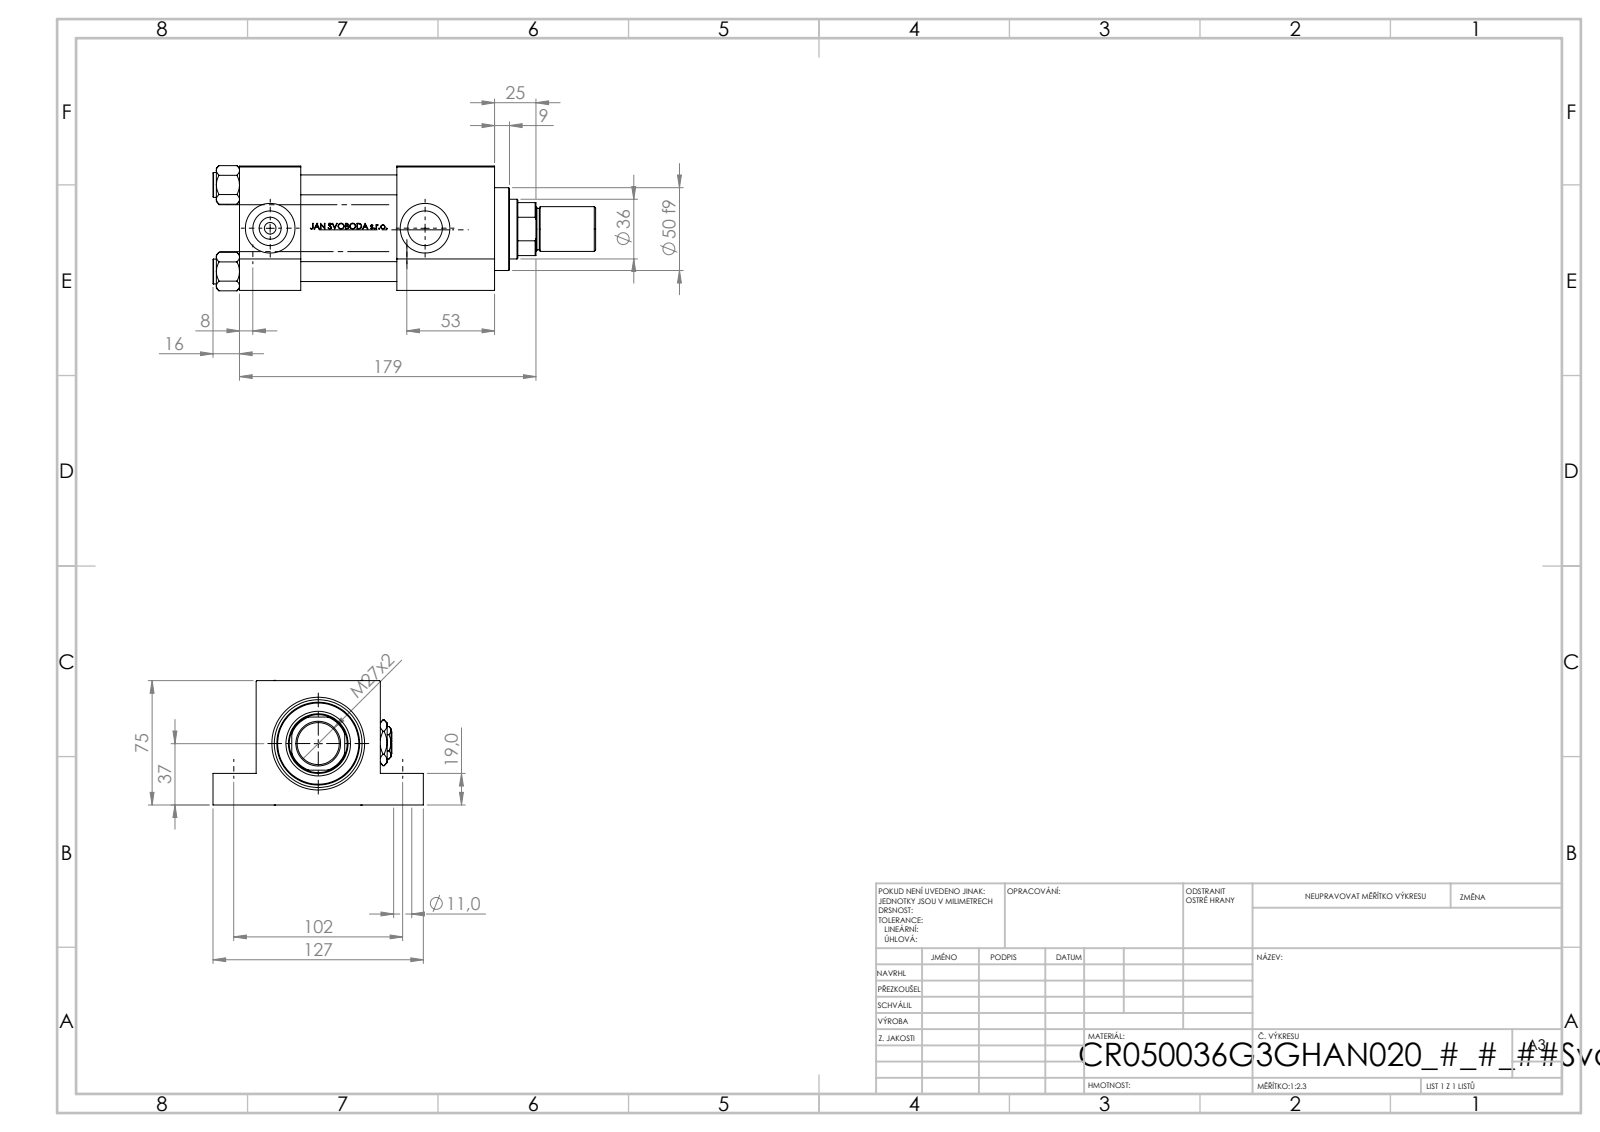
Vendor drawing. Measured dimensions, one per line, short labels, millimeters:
name: V215_VC_A; V215CR_VCP_G; Zatka_pro_OIL_PORT; V215CR_G_TYCINKA (+3 more)
written by: SolidWorks 2019 (CONFIG_CONTROL_DESIGN)
unit: mm
bodies: 14 solids, 1197 faces (481 planar, 136 cylindrical, 580 other)
size: 231 × 127 × 75.54
volume: 799 717 mm³; area: 176 388 mm²
holes: 4× ⌀12, 3× ⌀11, 2× ⌀7, 2× ⌀20.96, 2× ⌀30, 1× ⌀11, 1× ⌀25.5, 1× ⌀36, 1× ⌀39, 1× ⌀41, 1× ⌀53
bosses: 4× ⌀15, 1× ⌀56, 1× ⌀50, 1× ⌀27, 1× ⌀25
rounds: 1× R17.5
face distances: 75, 37, 19, 56, 154, 117, 59, 95, 58, 26
hole spacings: 52.3, 36.63, 37.34, 73.96, 102, 112, 151.49, 93.5
